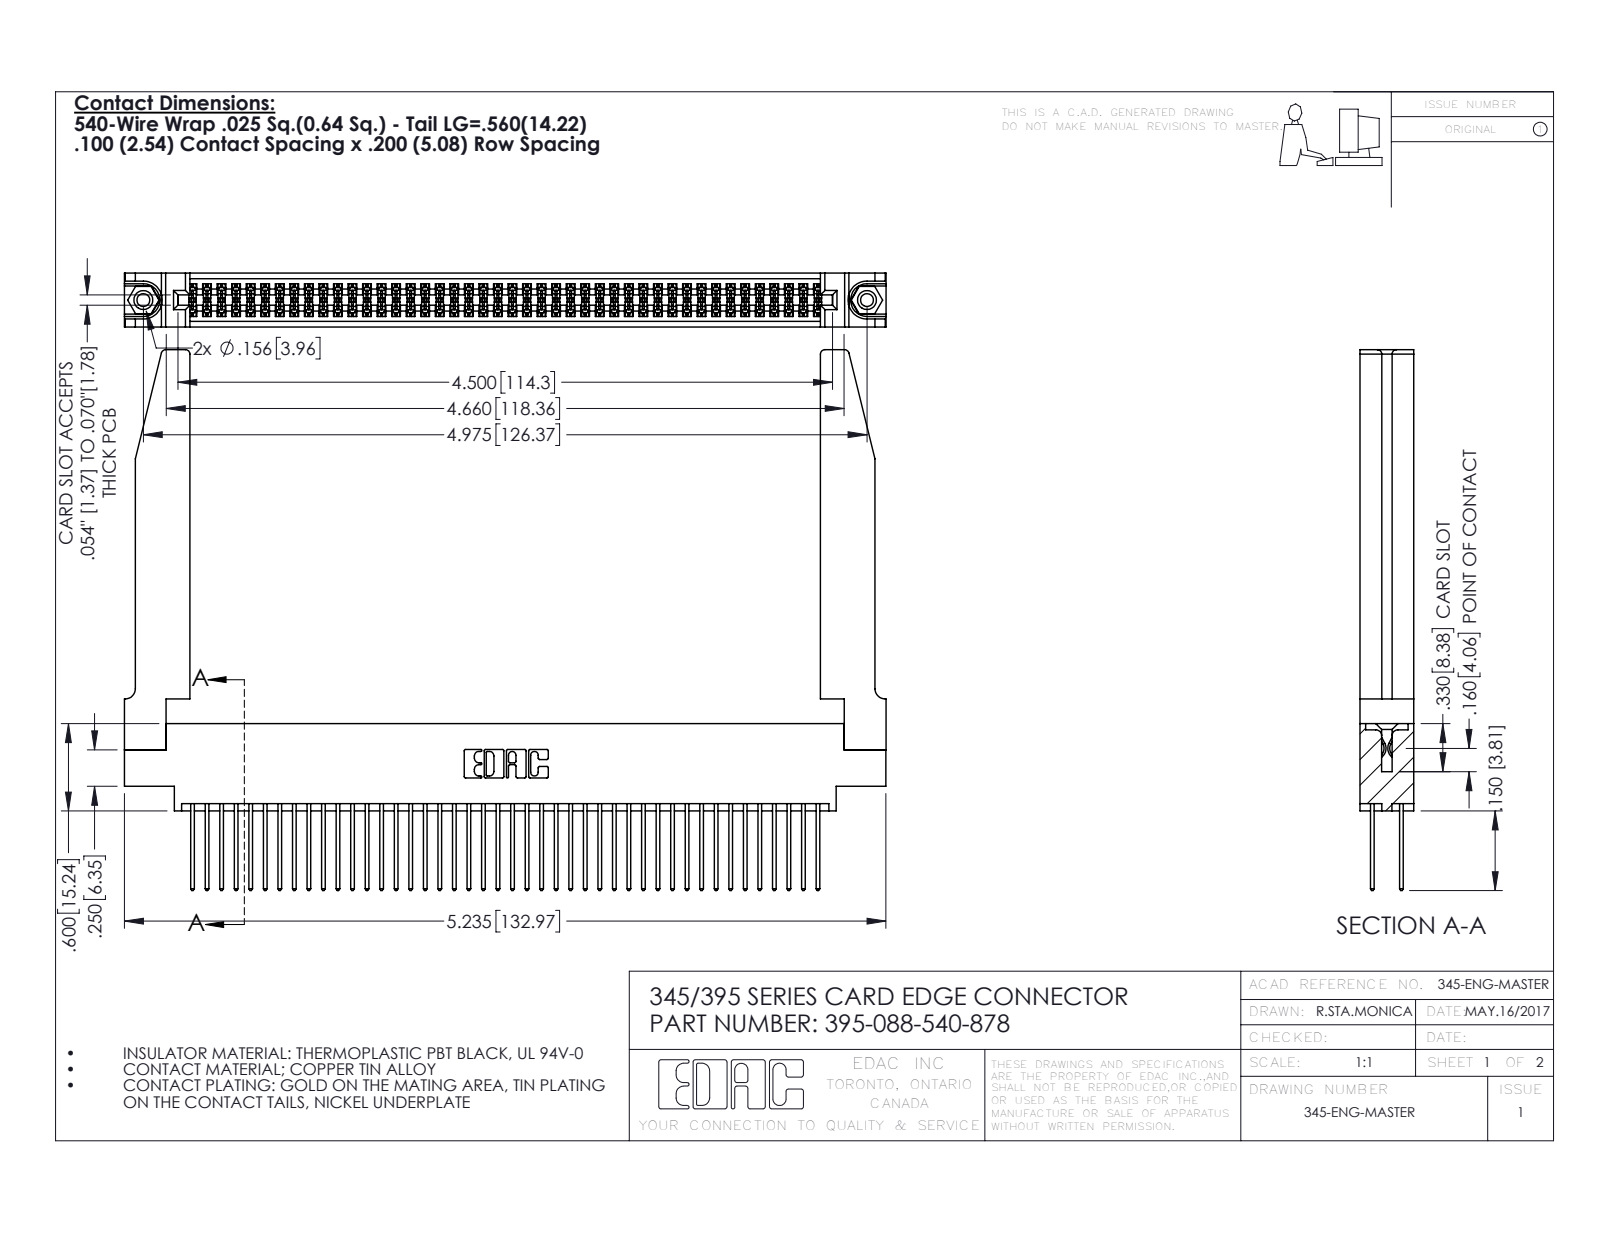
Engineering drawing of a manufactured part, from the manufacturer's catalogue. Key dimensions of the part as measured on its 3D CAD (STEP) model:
Part name (STEP PRODUCT): 345-292-001_345-293-140; 345-250-001_345-250-001-102; 345 Part_0.170 Offset - 0.156 Dia-TH; 345-220-078_345-220-078 (+1 more)
STEP written by: SolidWorks 2016 (CONFIG_CONTROL_DESIGN)
Units: inches
Bodies: 93 solids, 4764 faces (3130 planar, 1582 cylindrical, 52 other)
Overall size (bounding box): 5.236 × 3.717 × 0.37
Volume: 1.277 in³ · Surface area: 43.43 in²
Round holes (diameter × count): ⌀0.089 ×2, ⌀0.125 ×2, ⌀0.156 ×2, ⌀0.064 ×1
Round bosses / shafts (diameter × count): ⌀0.155 ×2
Partial cylindrical surfaces — rounded edges, fillets, slot ends (radius × count): R0.006 ×132, R0.01 ×88, R0.01 ×22, R0.03 ×8, R0.007 ×6, R0.031 ×6, R0.026 ×3, R0.014 ×2
Main face-to-face distances: 0.072, 0.298, 0.37, 0.2, 0.098, 0.272, 0.025, 0.225, 0.175, 0.148
Hole centre spacings: 0.27, 4.739, 4.975
